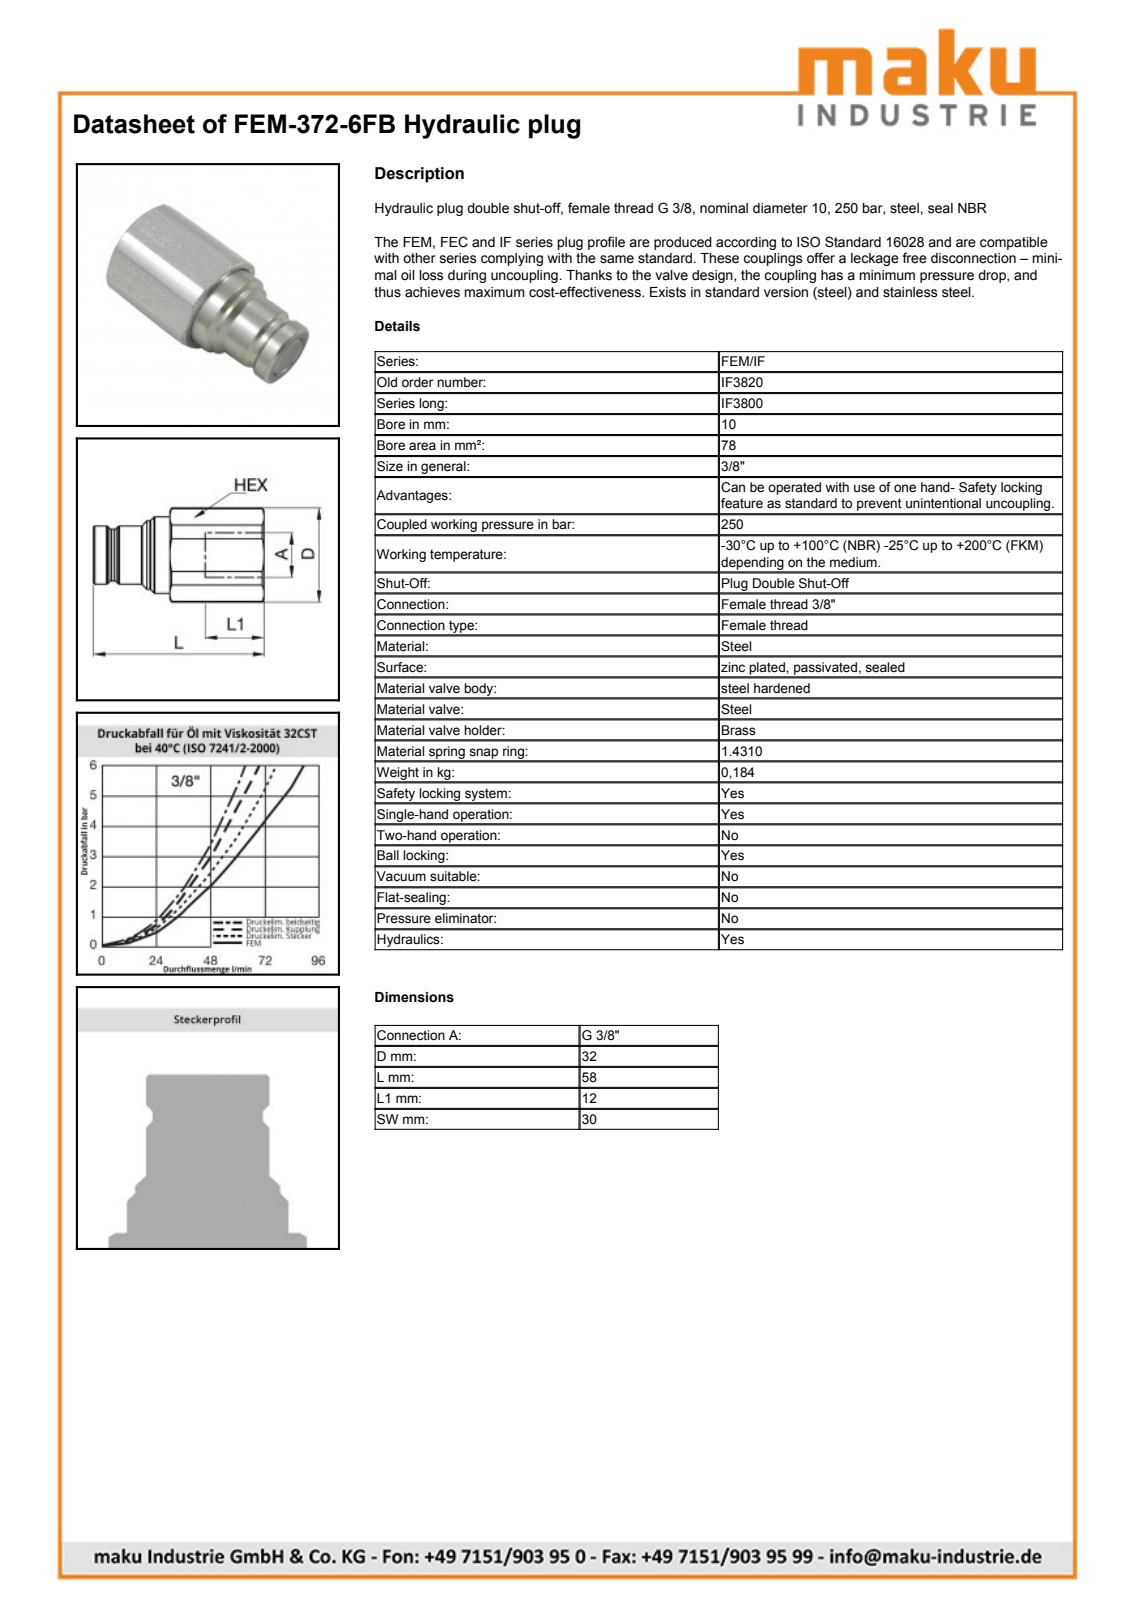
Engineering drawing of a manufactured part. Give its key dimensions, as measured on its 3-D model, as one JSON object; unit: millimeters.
{"part_name": "FEM-372-6FB", "step_written_by": "SolidWorks 2009 (AUTOMOTIVE_DESIGN)", "units": "millimeters", "bodies": {"solids": 1, "faces": 86, "planar": 12, "cylindrical": 24, "other": 50}, "overall_size": [58, 32, 30], "volume_mm3": 30587, "surface_area_mm2": 7427, "round_holes": [[12.65, 1], [14.5, 1], [15, 1], [26.2, 1]], "round_bosses_or_shafts": [[26, 1], [23.3, 1], [19.75, 1], [17.6, 1]], "partial_cylinders_radius": [[16, 1]], "face_to_face_distances": [30, 58, 40.61, 17.39, 26, 14.61, 32, 0.8, 25.2, 39.81]}
